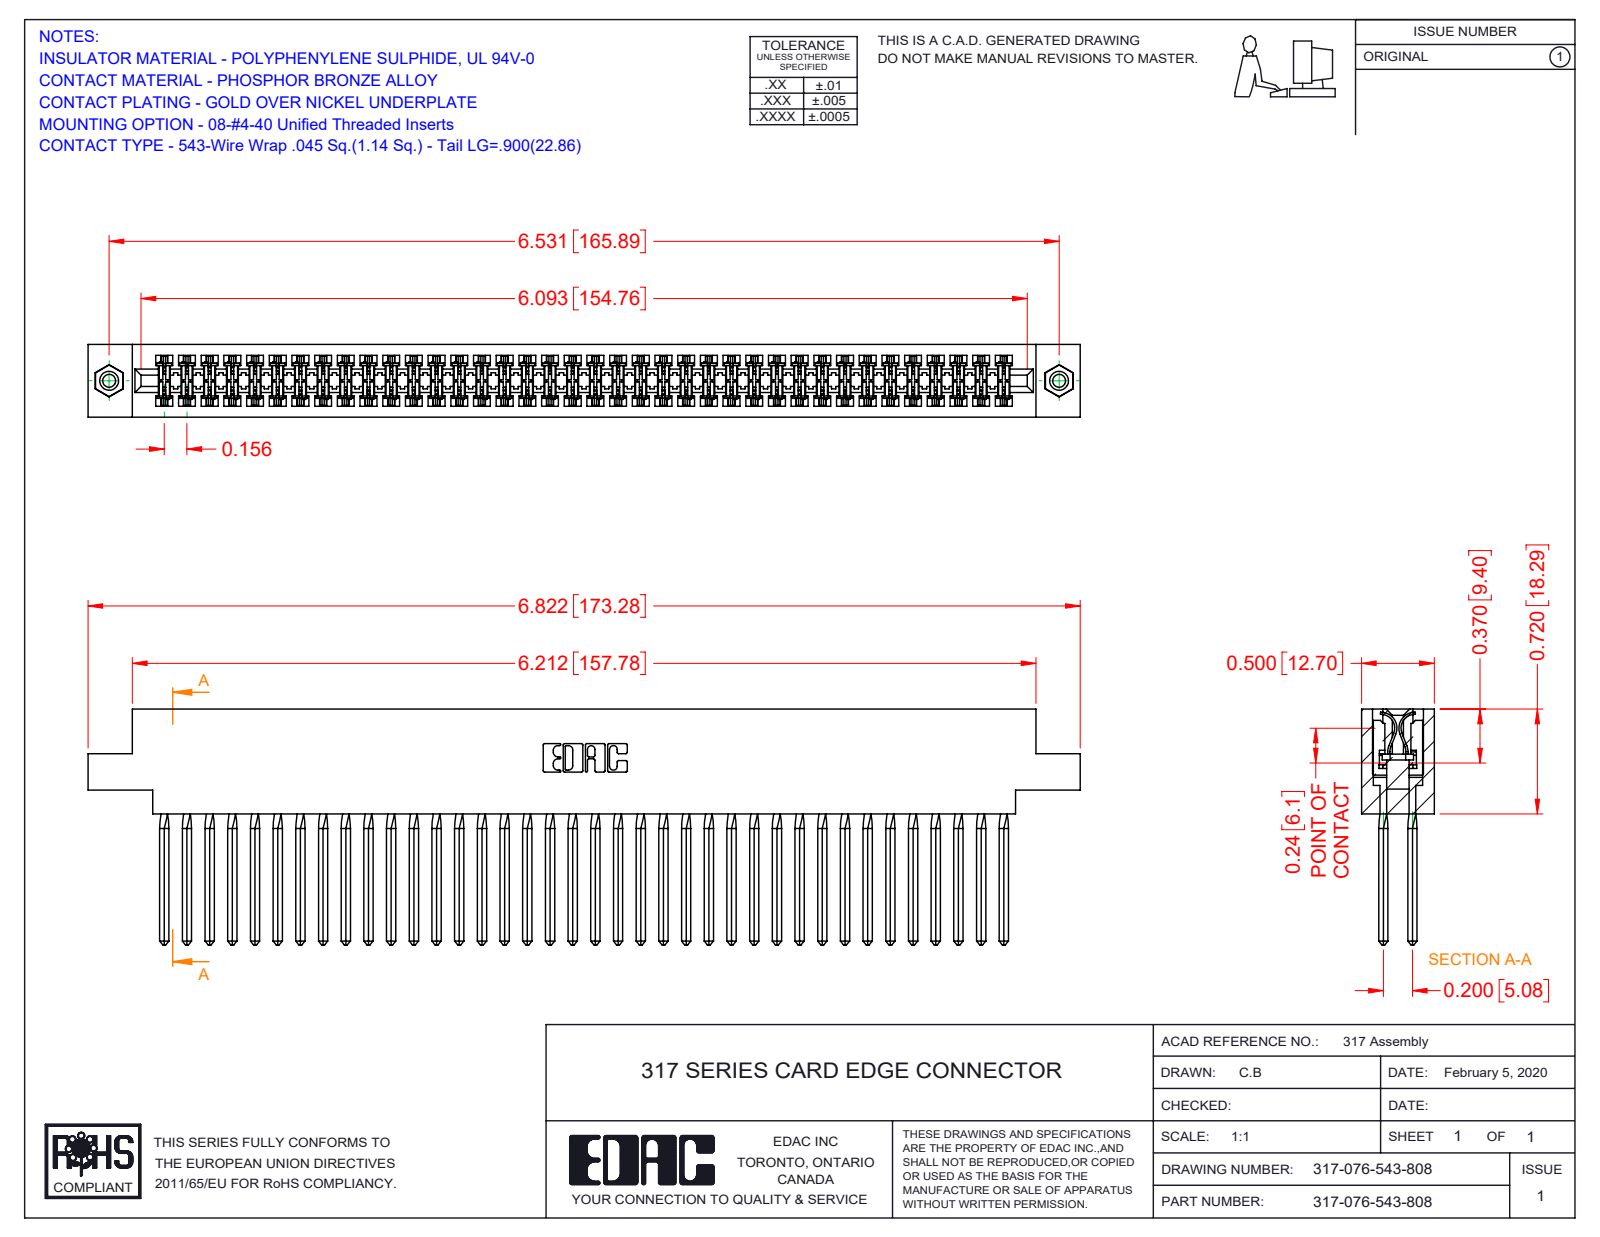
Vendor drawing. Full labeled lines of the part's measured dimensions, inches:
Part name (STEP PRODUCT): 317 Part_.156 Dia - TI; 317-076-543-808; 345-250-001_345-250-003-102; 317-290-001_543
STEP written by: SolidWorks 2016 (CONFIG_CONTROL_DESIGN)
Units: inches
Bodies: 79 solids, 6926 faces (5638 planar, 968 cylindrical, 320 other)
Overall size (bounding box): 6.822 × 1.62 × 0.5
Volume: 1.789 in³ · Surface area: 68.73 in²
Round holes (diameter × count): ⌀0.089 ×2, ⌀0.125 ×2, ⌀0.156 ×2
Round bosses / shafts (diameter × count): ⌀0.155 ×2
Partial cylindrical surfaces — rounded edges, fillets, slot ends (radius × count): R0.015 ×152, R0.01 ×22, R0.007 ×6, R0.031 ×6, R0.026 ×3, R0.095 ×2, R0.1 ×2, R0.11 ×2
Main face-to-face distances: 0.5, 0.075, 0.425, 0.35, 0.11, 0.195, 0.094, 0.2, 0.115, 0.131
Hole centre spacings: 6.531
